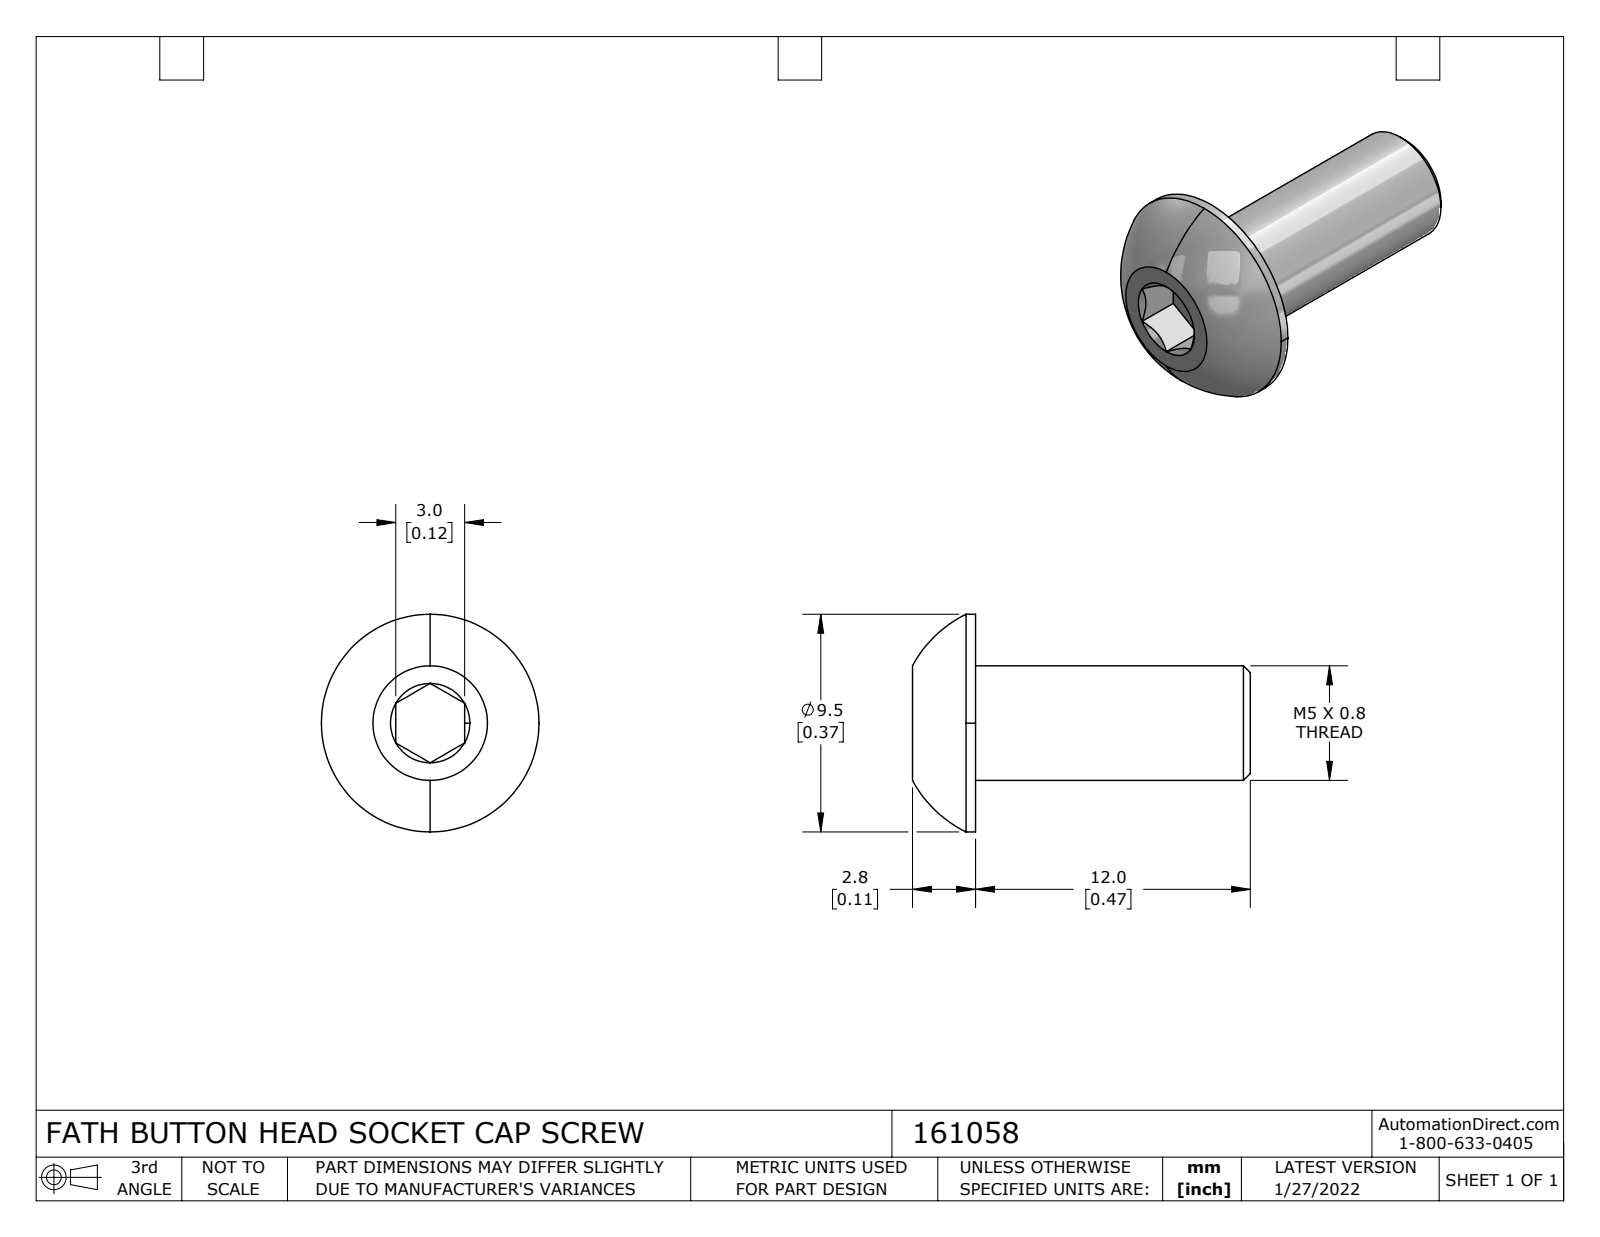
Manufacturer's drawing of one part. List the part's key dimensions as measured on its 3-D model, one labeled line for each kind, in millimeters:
Part name (STEP PRODUCT): 161058
STEP written by: SolidWorks 2021 (CONFIG_CONTROL_DESIGN)
Units: millimetres
Bodies: 1 solid, 25 faces (10 planar, 4 cylindrical, 11 other)
Overall size (bounding box): 14.75 × 9.5 × 9.5
Volume: 362 mm³ · Surface area: 385 mm²
Round bosses / shafts (diameter × count): ⌀9.5 ×1, ⌀5 ×1
Main face-to-face distances: 12, 14.75, 2.75, 3, 12.82, 0.82, 1.93
